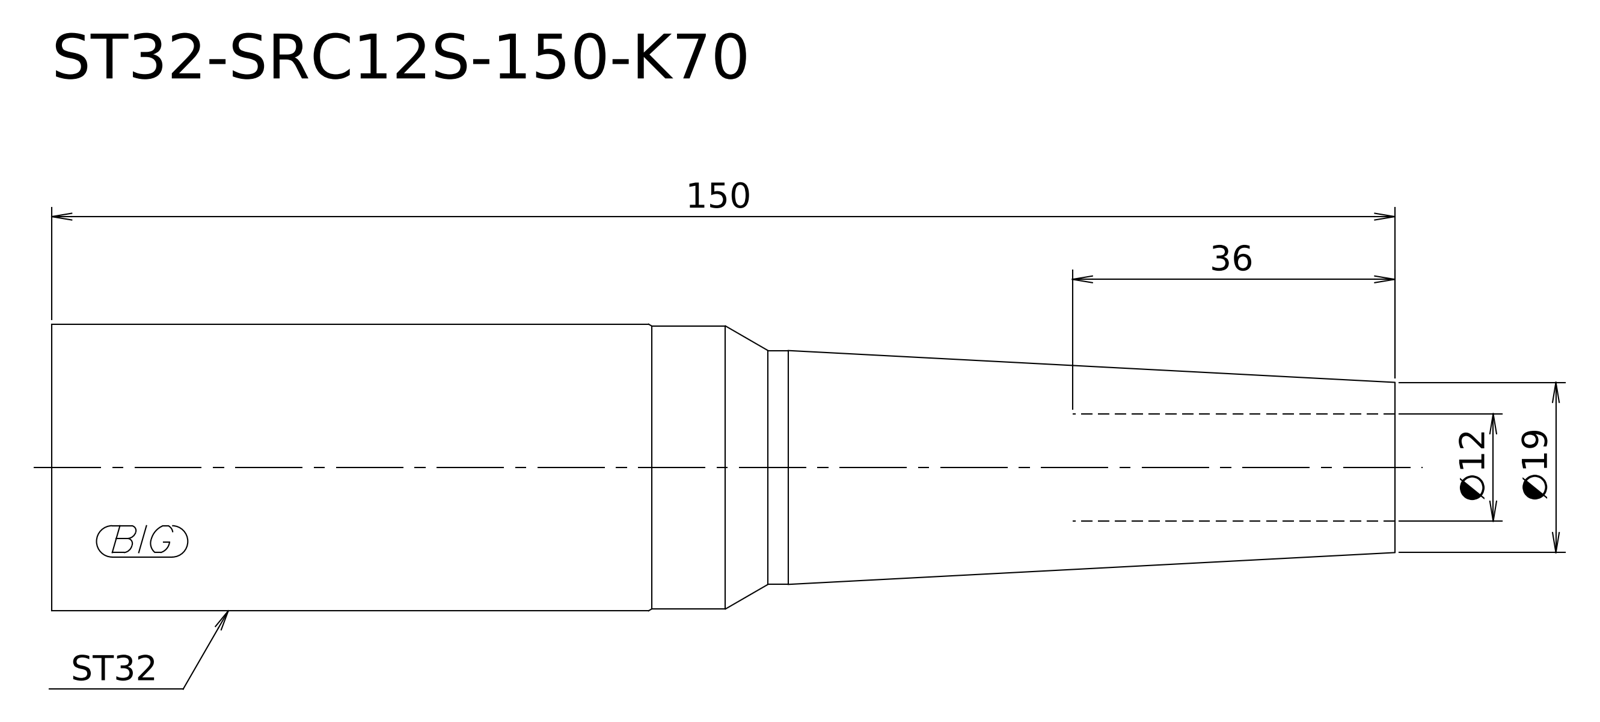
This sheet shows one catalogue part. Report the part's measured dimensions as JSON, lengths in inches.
{"step_written_by": "Kubotek KeyCreator V8.5.1 (14335) (CONFIG_CONTROL_DESIGN)", "units": "inches", "bodies": {"solids": 1, "faces": 8, "planar": 2, "cylindrical": 3, "other": 3}, "overall_size": [5.906, 1.26, 1.26], "volume_in3": 5.611, "surface_area_in2": 21.91, "round_bosses_or_shafts": [[1.26, 1], [1.244, 1], [1.028, 1]], "face_to_face_distances": [5.906]}
